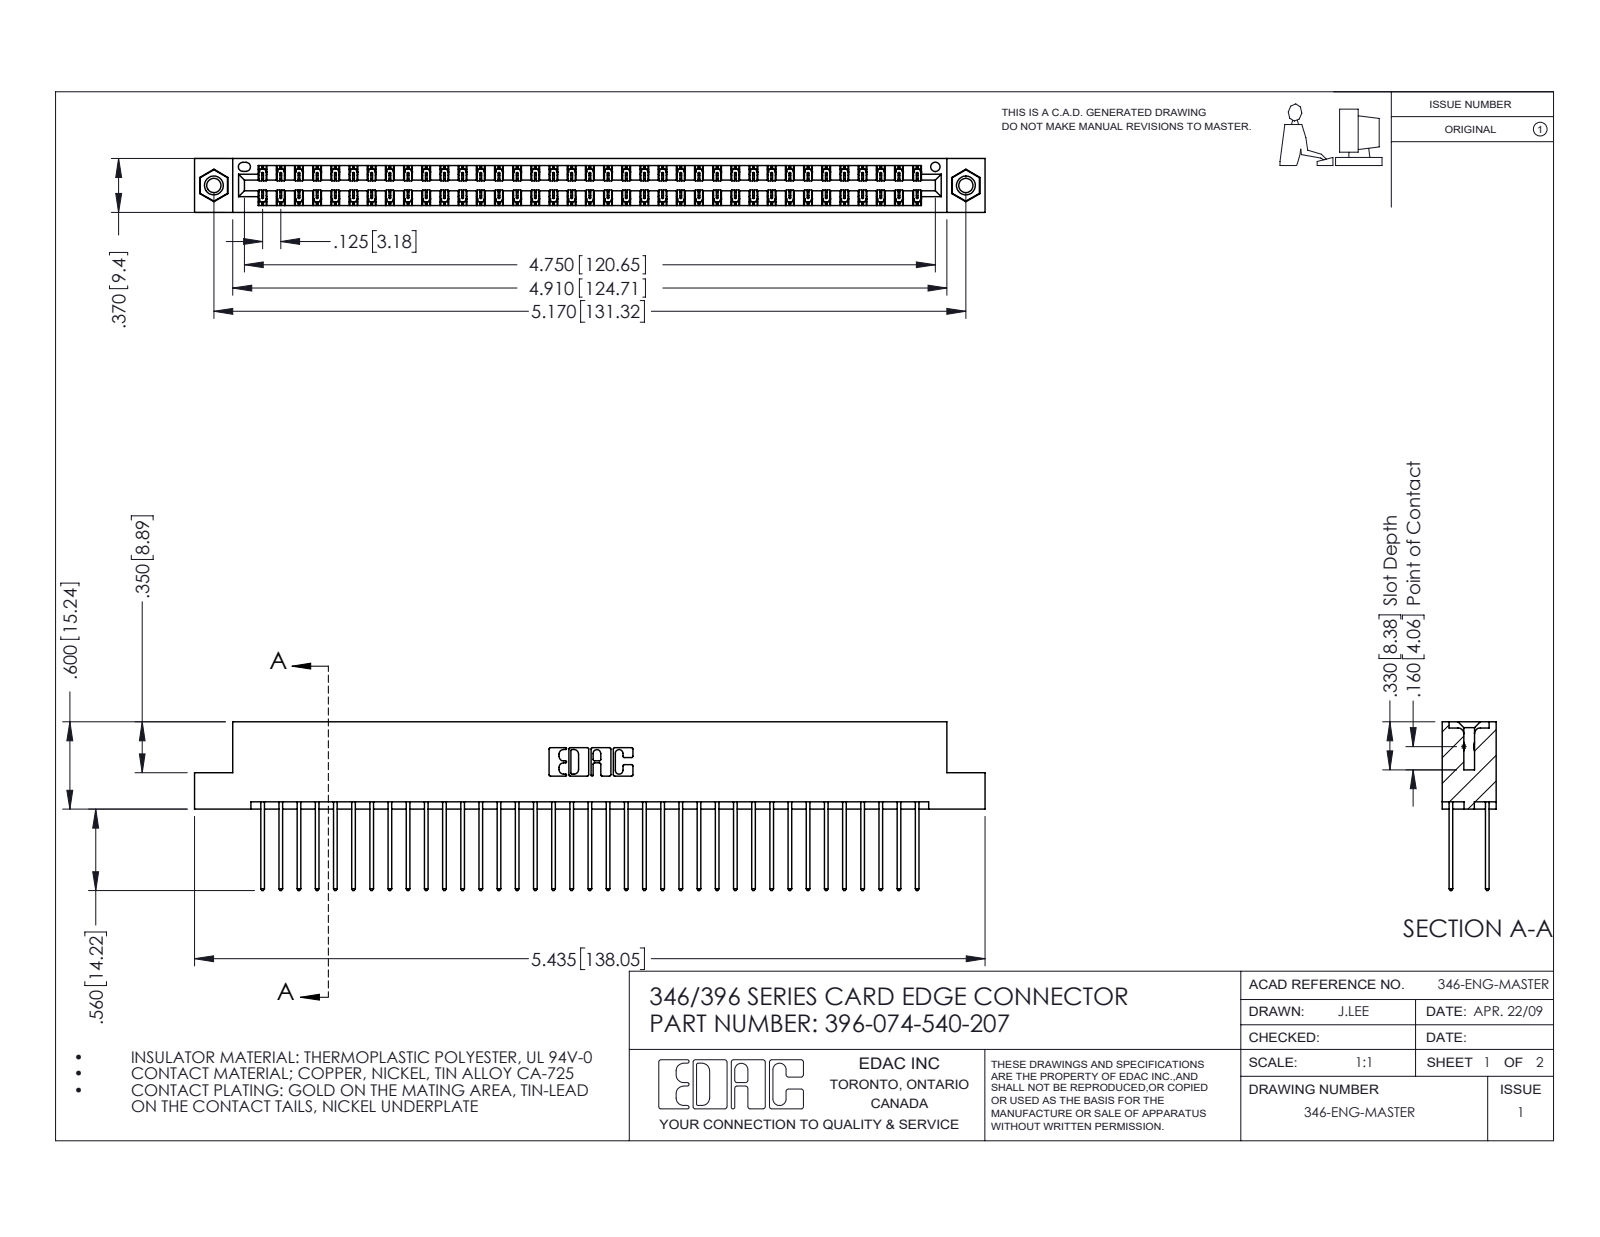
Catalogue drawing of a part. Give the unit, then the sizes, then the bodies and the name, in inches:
Units: inches
Overall size (bounding box): 5.435 × 1.16 × 0.37
Round holes (diameter × count): ⌀0.098 ×2, ⌀0.125 ×2, ⌀0.156 ×2, ⌀0.064 ×1
Round bosses / shafts (diameter × count): ⌀0.155 ×2
Partial cylindrical surfaces — rounded edges, fillets, slot ends (radius × count): R0.006 ×111, R0.01 ×74, R0.01 ×22, R0.007 ×6, R0.031 ×6, R0.026 ×3, R0.014 ×2, R0.022 ×2
Main face-to-face distances: 0.048, 0.322, 0.25, 0.072, 0.298, 0.025, 0.37, 0.275, 0.148, 0.222
Hole centre spacings: 0.246, 4.961, 5.17
Volume: 0.835 in³ · Surface area: 31.15 in²
Bodies: 77 solids, 4030 faces (2698 planar, 1316 cylindrical, 16 other)
Part name (STEP PRODUCT): 345-292-001_345-293-140; 396-074-540-207; 346 Part_Flush Mounting Lugs - 0.156 Dia-TI; 345-250-001_345-250-005-103
STEP written by: SolidWorks 2016 (CONFIG_CONTROL_DESIGN)
